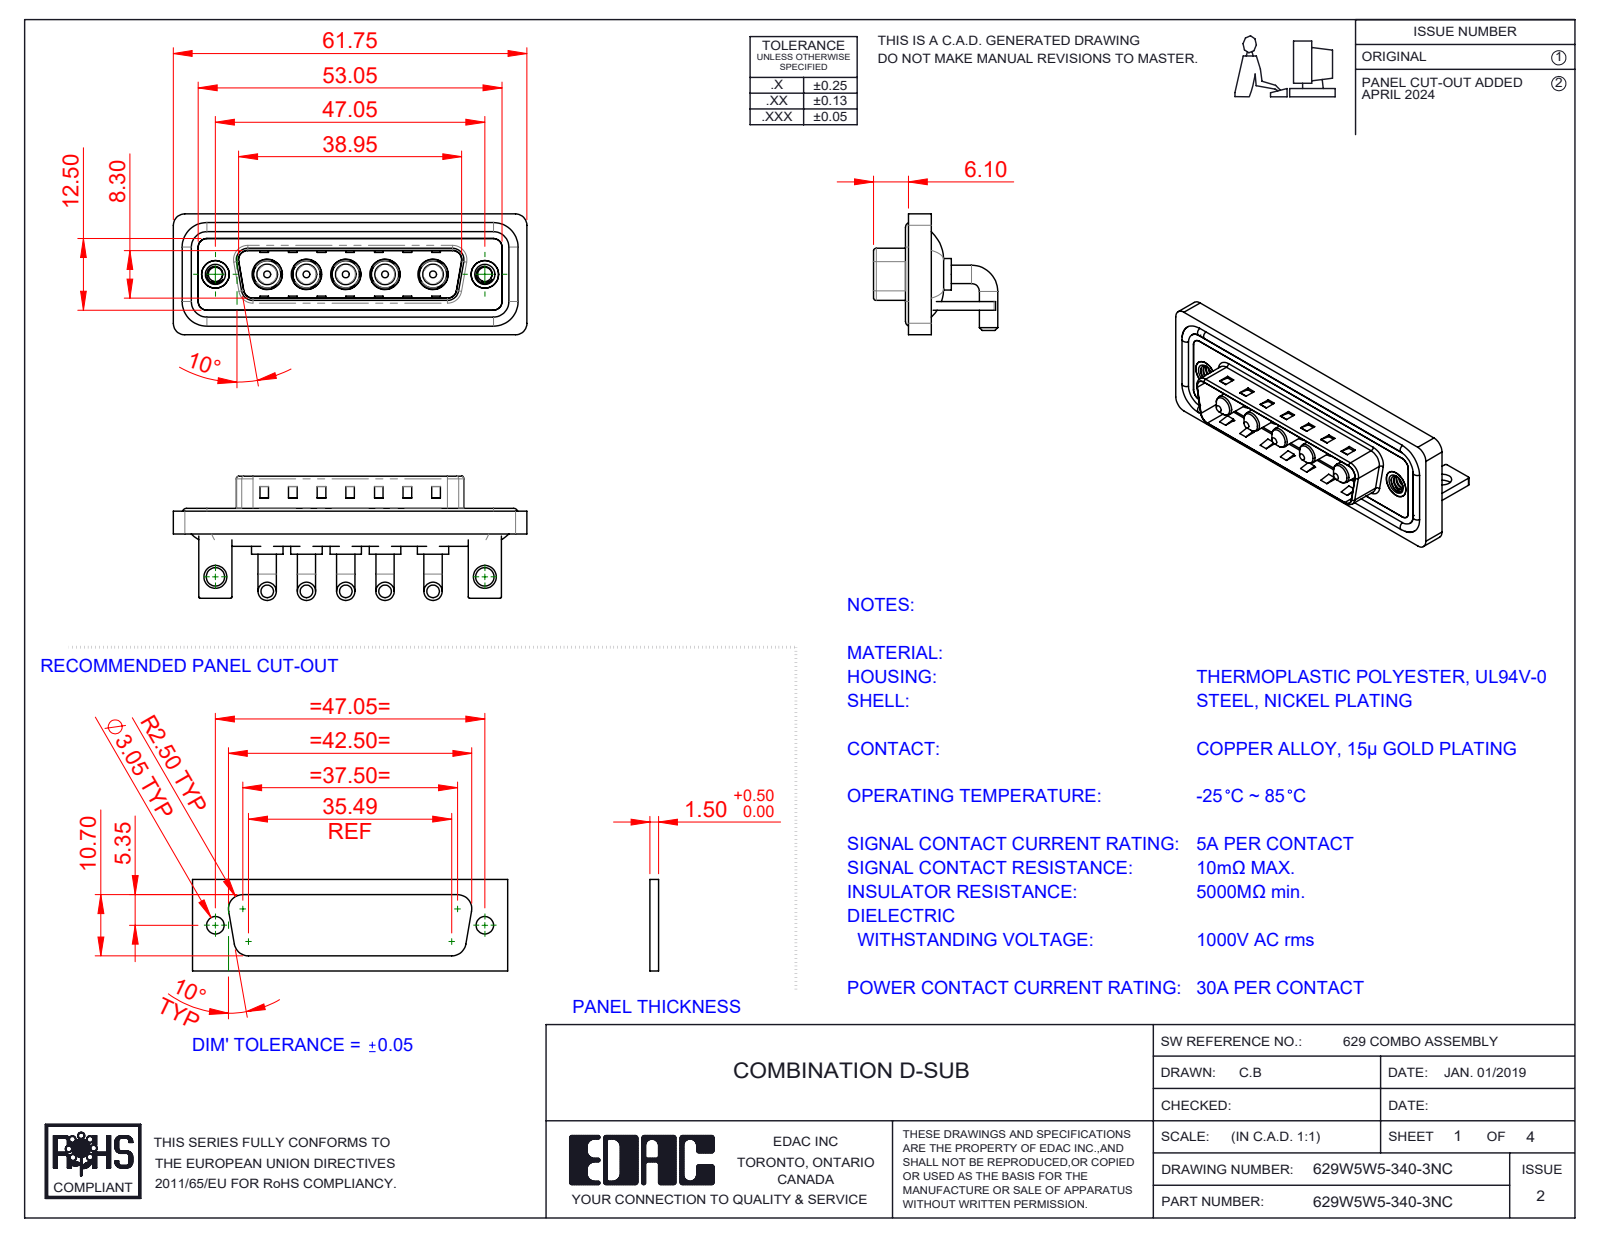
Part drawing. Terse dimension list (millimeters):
name: 629Combo Stabilizer Bracket; 629Combo Shell Rear_25 Contacts; 629Combo Shell Front_25 Contacts; 629Combo Housing_5W5 (+4 more)
written by: SolidWorks 2023 (CONFIG_CONTROL_DESIGN)
unit: mm
bodies: 19 solids, 736 faces (279 planar, 311 cylindrical, 146 other)
size: 61.75 × 21.7 × 21.1
volume: 8 214 mm³; area: 12 952 mm²
holes: 5× ⌀4.85, 5× ⌀5.3, 2× ⌀2.5, 2× ⌀3.2, 2× ⌀4, 2× ⌀4.8, 2× ⌀5
bosses: 10× ⌀3.2, 5× ⌀5.5, 5× ⌀5.2, 5× ⌀4.75, 5× ⌀3.75, 5× ⌀3.6, 4× ⌀1.6, 2× ⌀4.9
rounds: 19× R2, 18× R1.5, 16× R0.25, 9× R0.5, 8× R1.6, 5× R2.1, 4× R0.6, 4× R0.65
face distances: 0.4, 1.5, 2.9, 0.8, 2.1, 3.7, 1.1, 4.5, 4.1, 1.2
hole spacings: 6.86, 13.73, 47.05, 6.85, 6.87, 8.37, 8.38, 9.04
